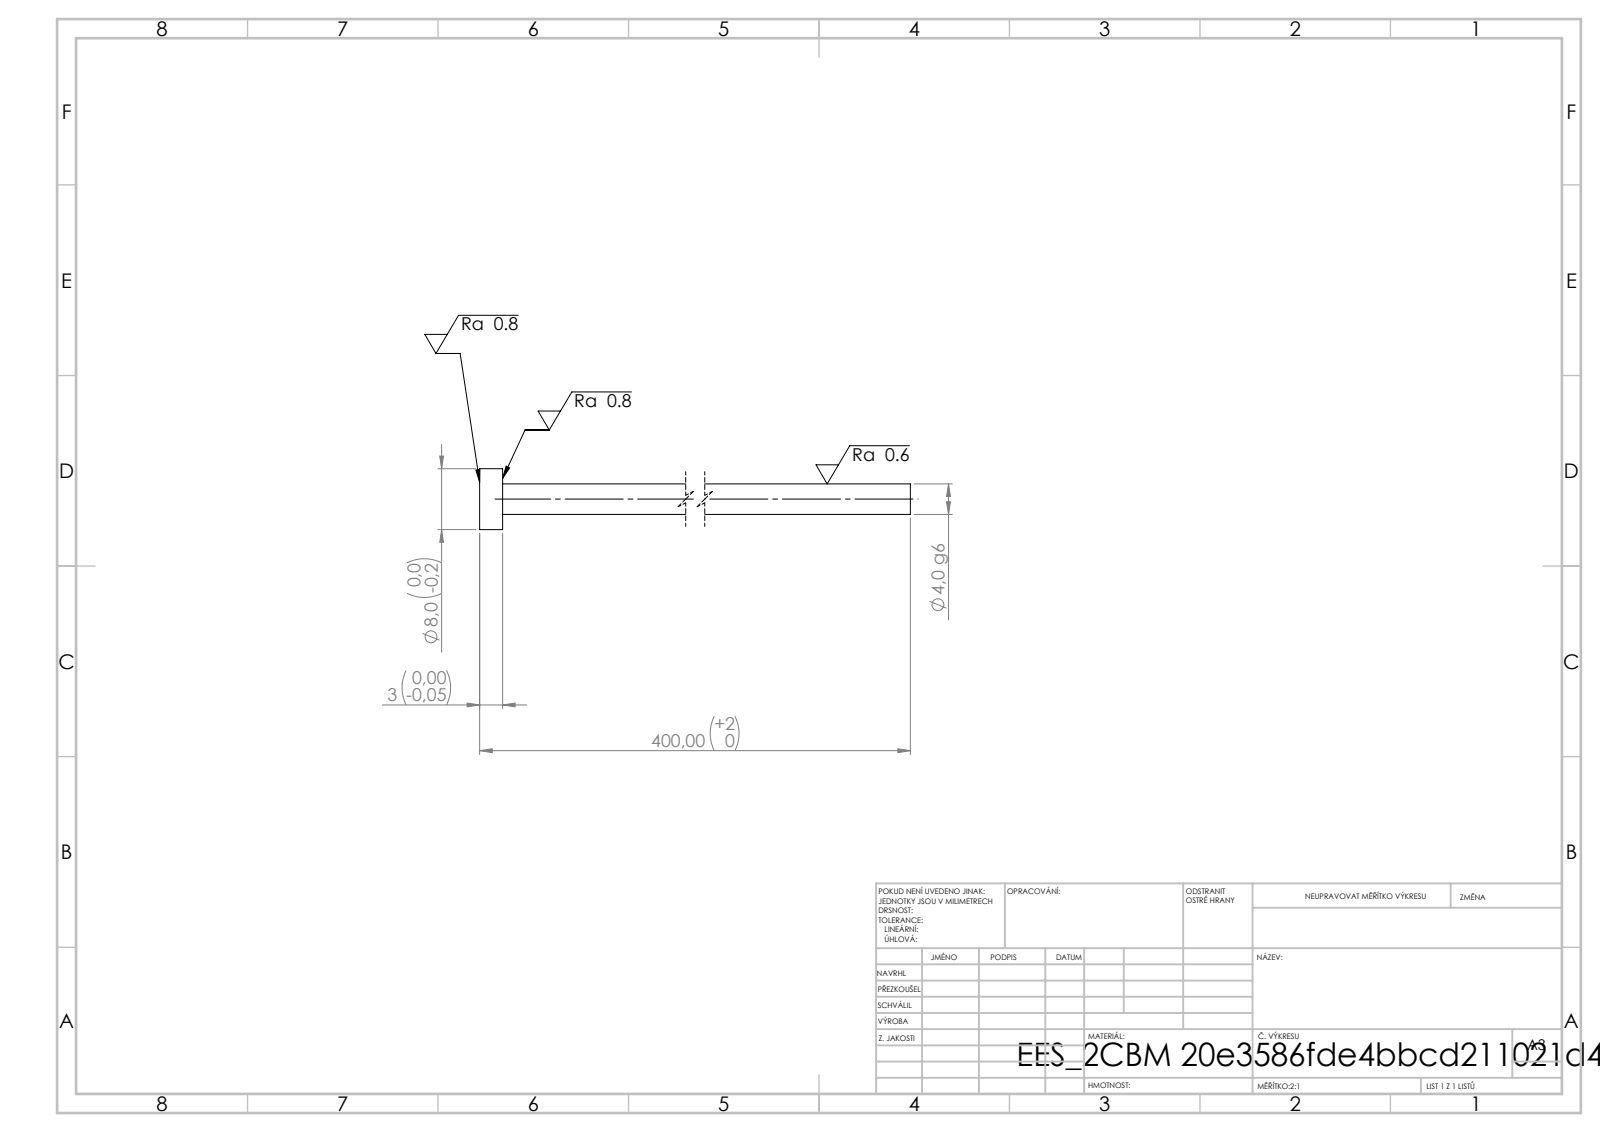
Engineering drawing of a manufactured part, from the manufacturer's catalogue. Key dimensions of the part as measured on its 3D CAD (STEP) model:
STEP written by: SolidWorks 2019 (CONFIG_CONTROL_DESIGN)
Units: millimetres
Bodies: 1 solid, 7 faces (3 planar, 4 cylindrical, 0 other)
Overall size (bounding box): 400 × 8 × 8
Volume: 5 140 mm³ · Surface area: 5 165 mm²
Round bosses / shafts (diameter × count): ⌀8 ×1, ⌀4 ×1
Main face-to-face distances: 3, 400, 397
